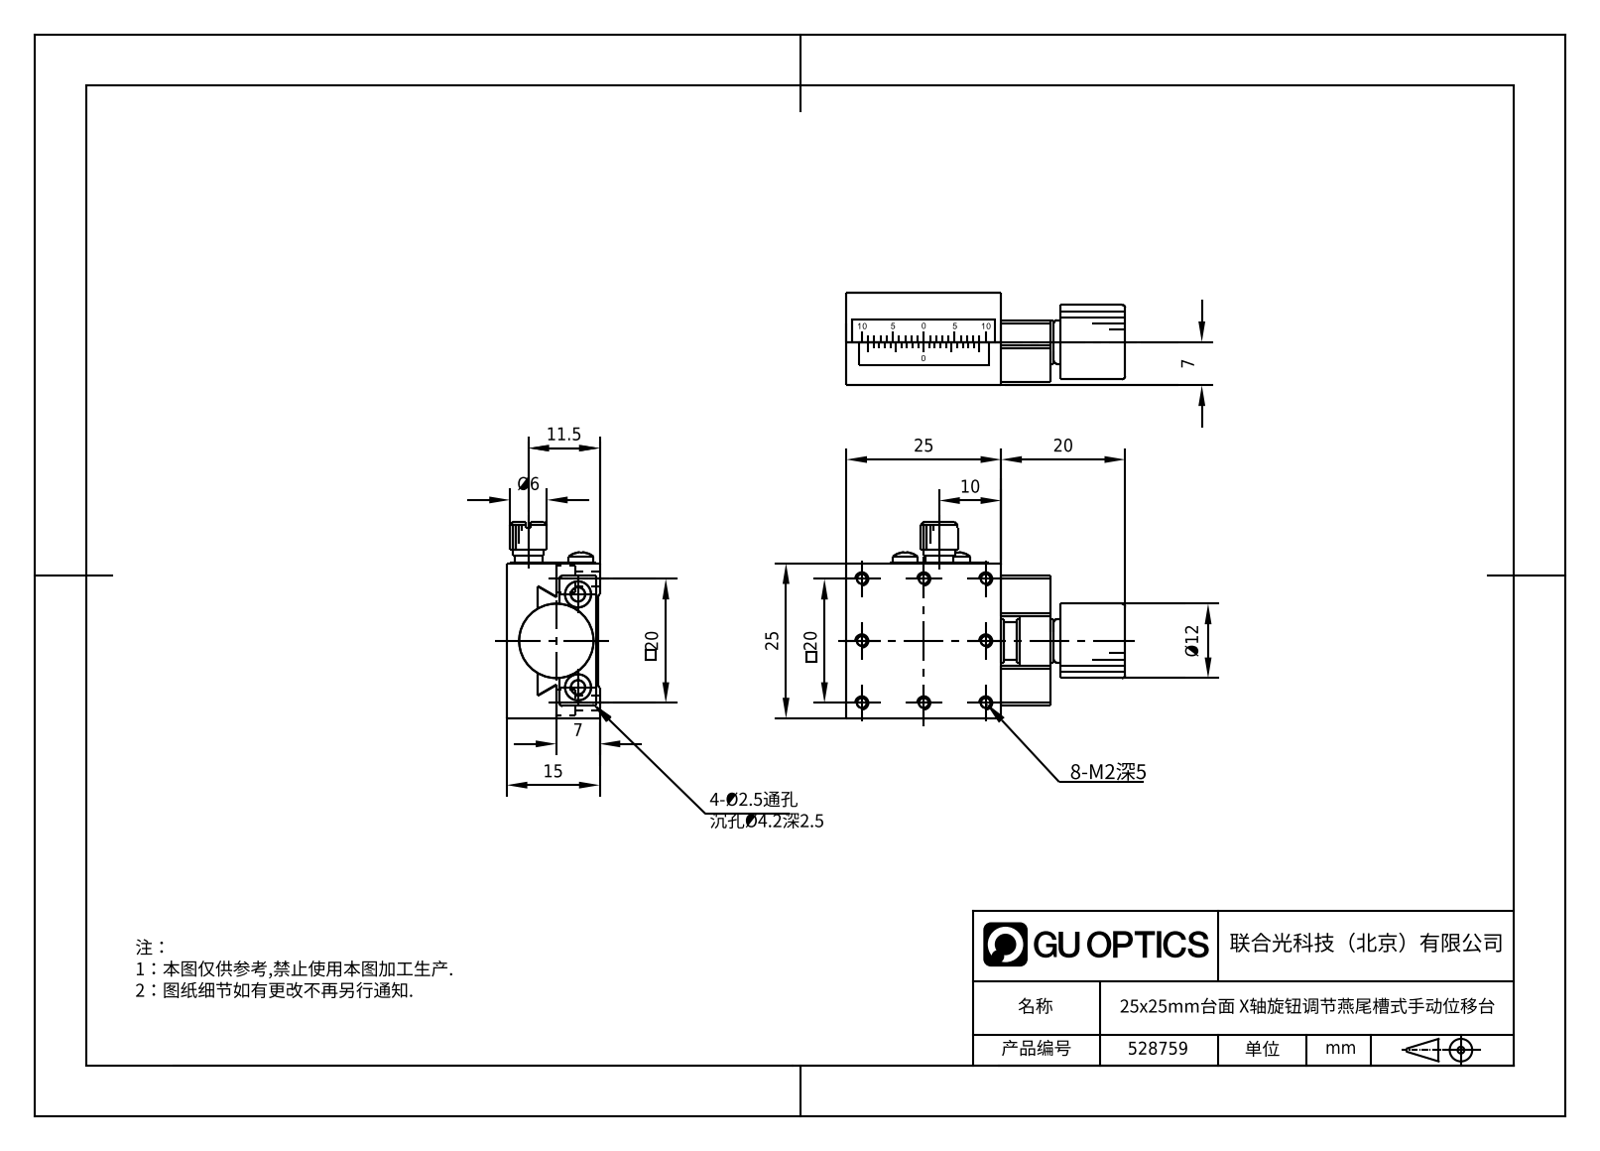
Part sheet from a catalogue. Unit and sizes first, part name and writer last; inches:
Units: inches
Overall size (bounding box): 1.772 × 1.321 × 0.591
Round holes (diameter × count): ⌀0.062 ×12, ⌀0.098 ×10, ⌀0.157 ×5, ⌀0.062 ×4, ⌀0.165 ×4, ⌀0.087 ×2, ⌀0.079 ×1, ⌀0.097 ×1, ⌀0.276 ×1
Round bosses / shafts (diameter × count): ⌀0.236 ×2, ⌀0.157 ×1, ⌀0.118 ×1, ⌀0.079 ×1
Partial cylindrical surfaces — rounded edges, fillets, slot ends (radius × count): R0.039 ×8, R0.049 ×2, R0.236 ×1
Main face-to-face distances: 0.315, 0.157, 0.02, 0.276, 0.591, 0.098, 0.413, 0.177, 0.984, 0.295
Hole centre spacings: 0.394, 0.88, 0.787, 0.411, 0.481, 0.557, 0.646, 0.276
Volume: 0.625 in³ · Surface area: 13.13 in²
Bodies: 3 solids, 460 faces (198 planar, 116 cylindrical, 146 other)
Part name (STEP PRODUCT): 528759
STEP written by: SolidWorks 2020 (CONFIG_CONTROL_DESIGN)
